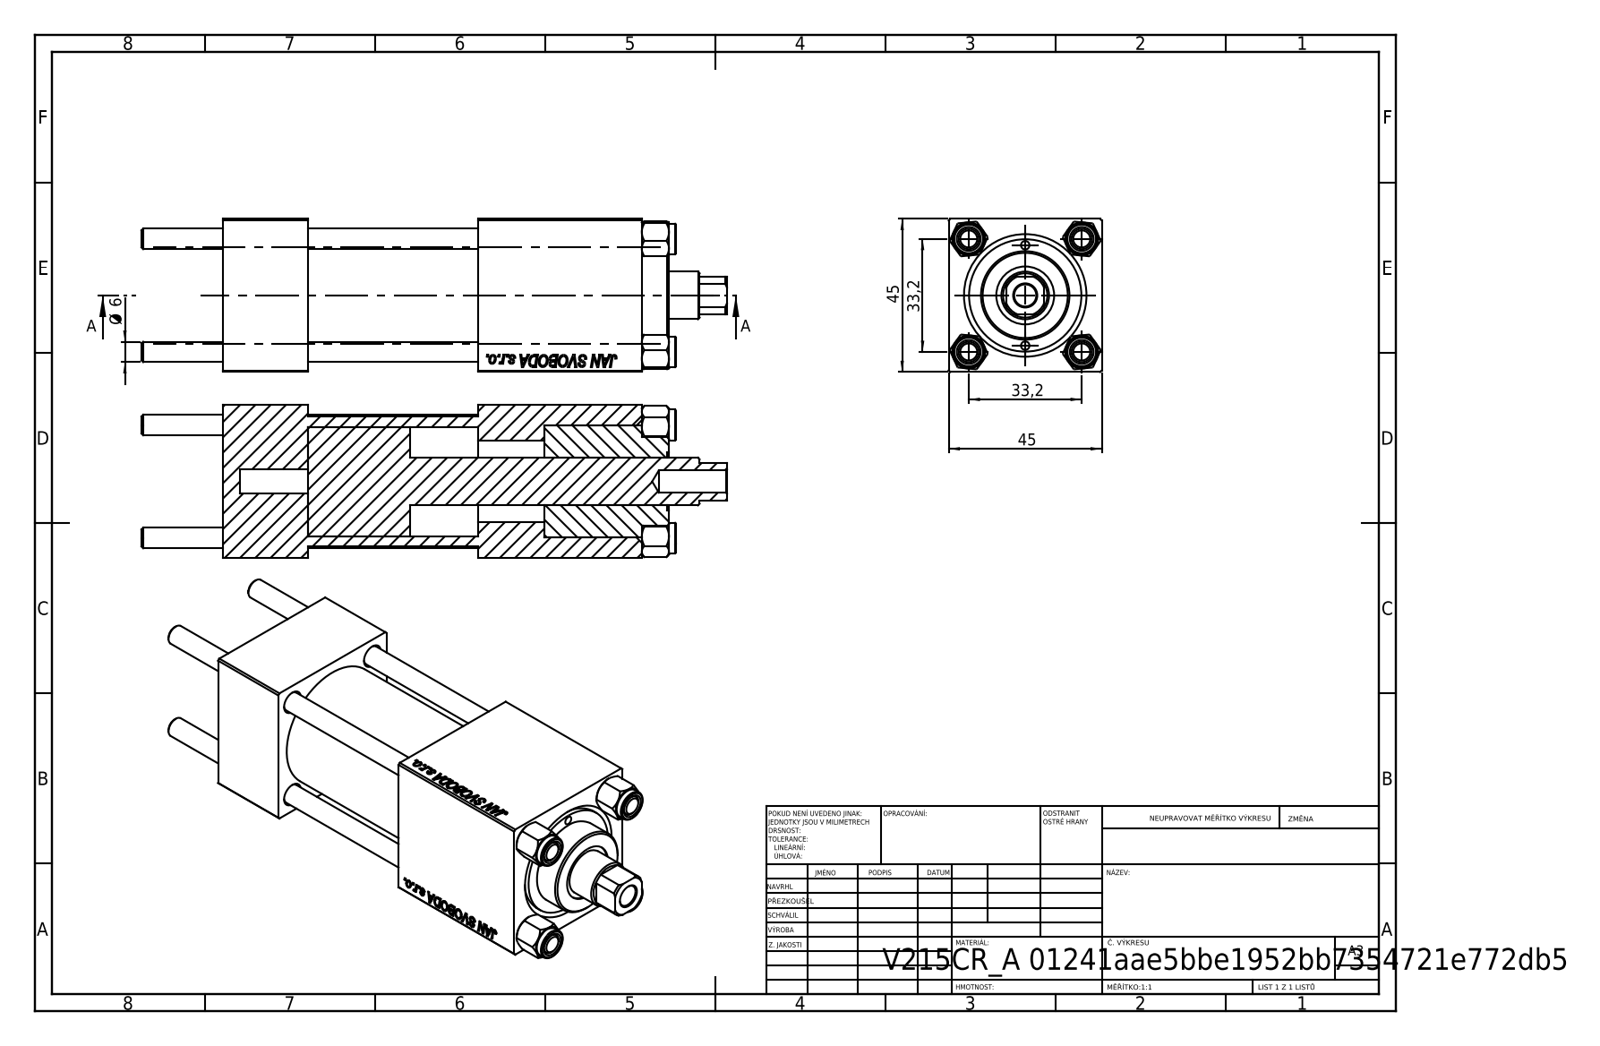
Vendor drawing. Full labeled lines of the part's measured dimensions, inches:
Part name (STEP PRODUCT): V215_VC_A; V215CR_BODY_A; V215CR_VCP; NUT_M5 (+1 more)
STEP written by: SolidWorks 2019 (CONFIG_CONTROL_DESIGN)
Units: inches
Bodies: 11 solids, 1139 faces (521 planar, 82 cylindrical, 536 other)
Overall size (bounding box): 6.772 × 1.772 × 1.772
Volume: 12.1 in³ · Surface area: 113 in²
Round holes (diameter × count): ⌀0.236 ×4, ⌀0.098 ×2, ⌀0.276 ×2, ⌀0.518 ×2, ⌀0.787 ×2, ⌀0.256 ×1, ⌀0.551 ×1, ⌀0.669 ×1, ⌀0.945 ×1, ⌀1.26 ×1, ⌀1.299 ×1
Round bosses / shafts (diameter × count): ⌀0.354 ×4, ⌀1.496 ×1, ⌀1.024 ×1
Partial cylindrical surfaces — rounded edges, fillets, slot ends (radius × count): R0.256 ×1
Main face-to-face distances: 1.772, 0.984, 4.843, 3.858, 1.969, 2.953, 1.89, 3.713, 2.728, 0.76
Hole centre spacings: 0.657, 0.924, 1.307, 1.396, 0.581, 1.848, 1.161, 2.972
